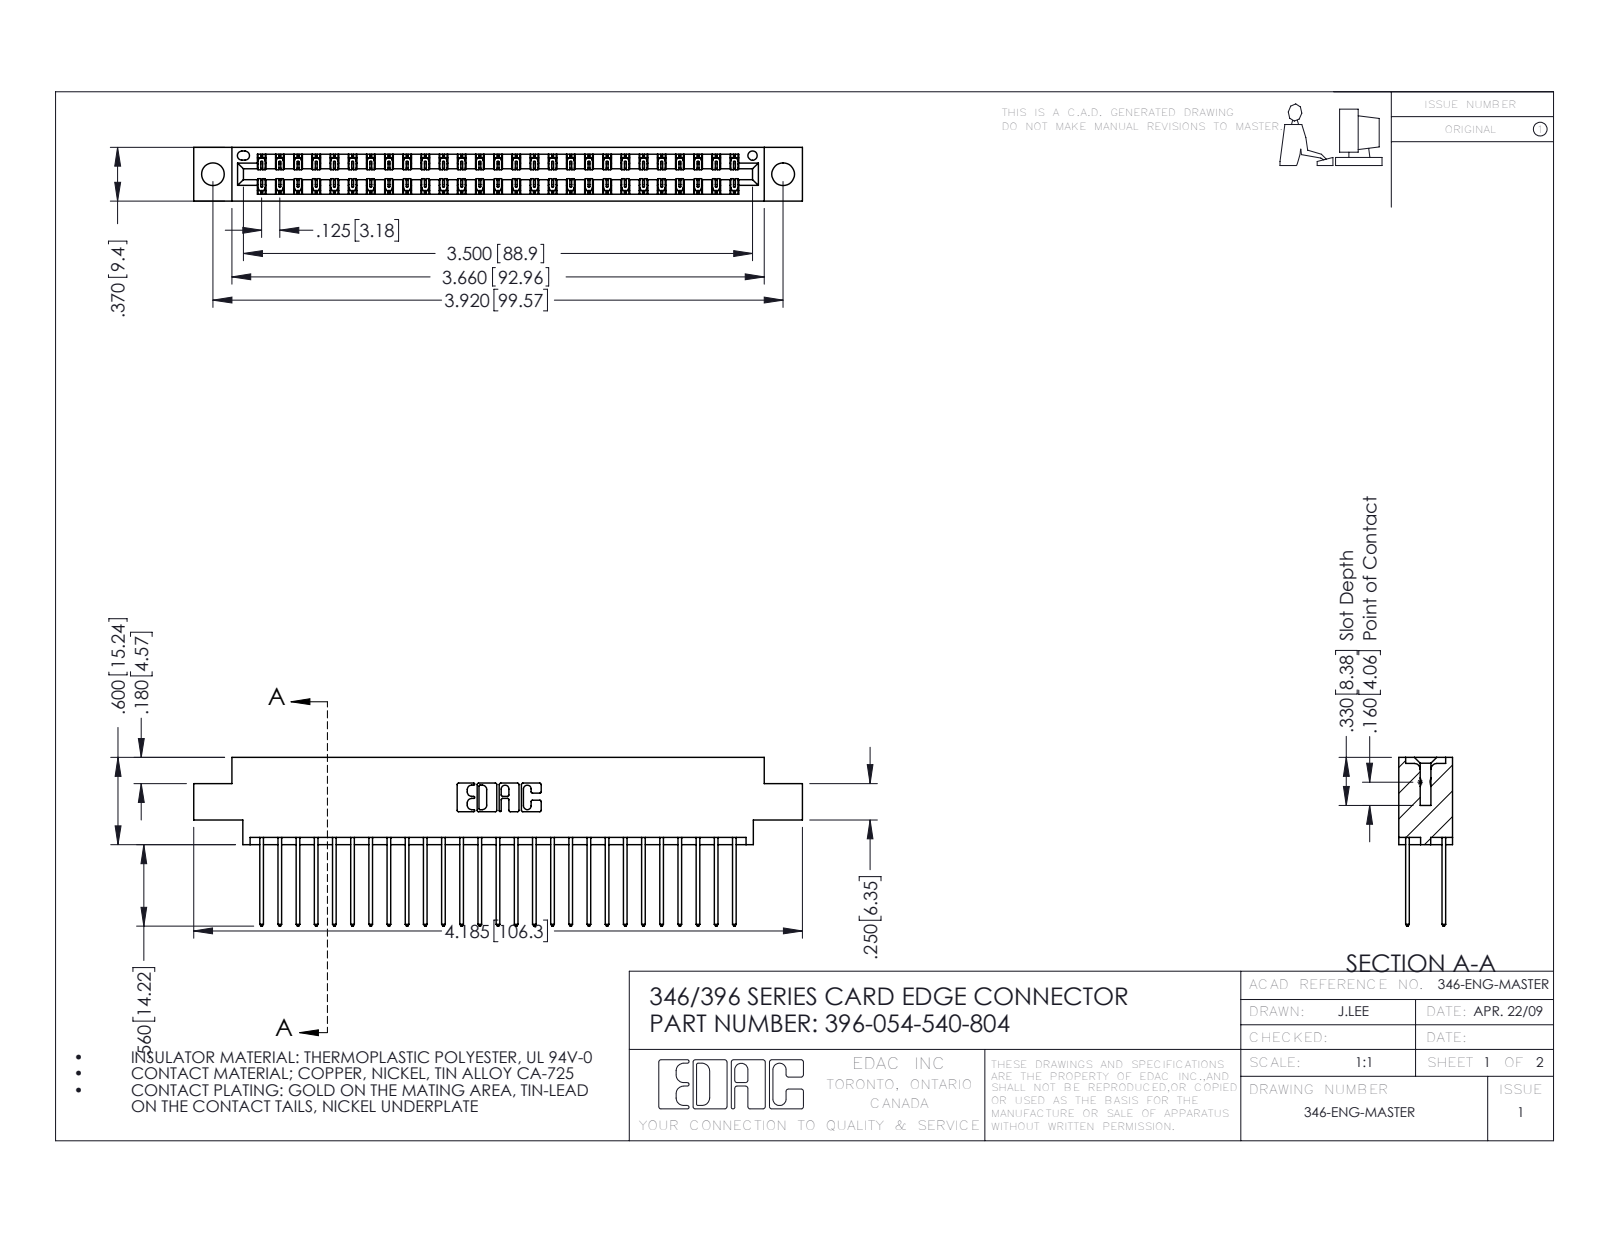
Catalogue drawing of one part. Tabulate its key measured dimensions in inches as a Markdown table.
| quantity | value |
| --- | --- |
| part name | 345-292-001_345-293-140; 396-054-540-804; 346 Part_0.170 Offset - 0.156 Dia-TH |
| STEP written by | SolidWorks 2016 (CONFIG_CONTROL_DESIGN) |
| units | inches |
| bodies | 55 solids, 2934 faces (1970 planar, 964 cylindrical, 0 other) |
| overall size | 4.185 × 1.16 × 0.37 |
| volume | 0.623 in³ |
| surface area | 22.88 in² |
| round holes (diameter × count) | 0.156 × 2, 0.064 × 1 |
| partial cylindrical surfaces (radius × count) | 0.006 × 81, 0.01 × 54, 0.01 × 22, 0.007 × 6, 0.031 × 6, 0.026 × 3, 0.014 × 2, 0.022 × 2 |
| main face-to-face distances | 0.048, 0.322, 0.25, 0.37, 0.072, 0.298, 0.025, 0.275, 0.148, 0.222 |
| hole center spacings | 0.246, 3.712, 3.92 |
